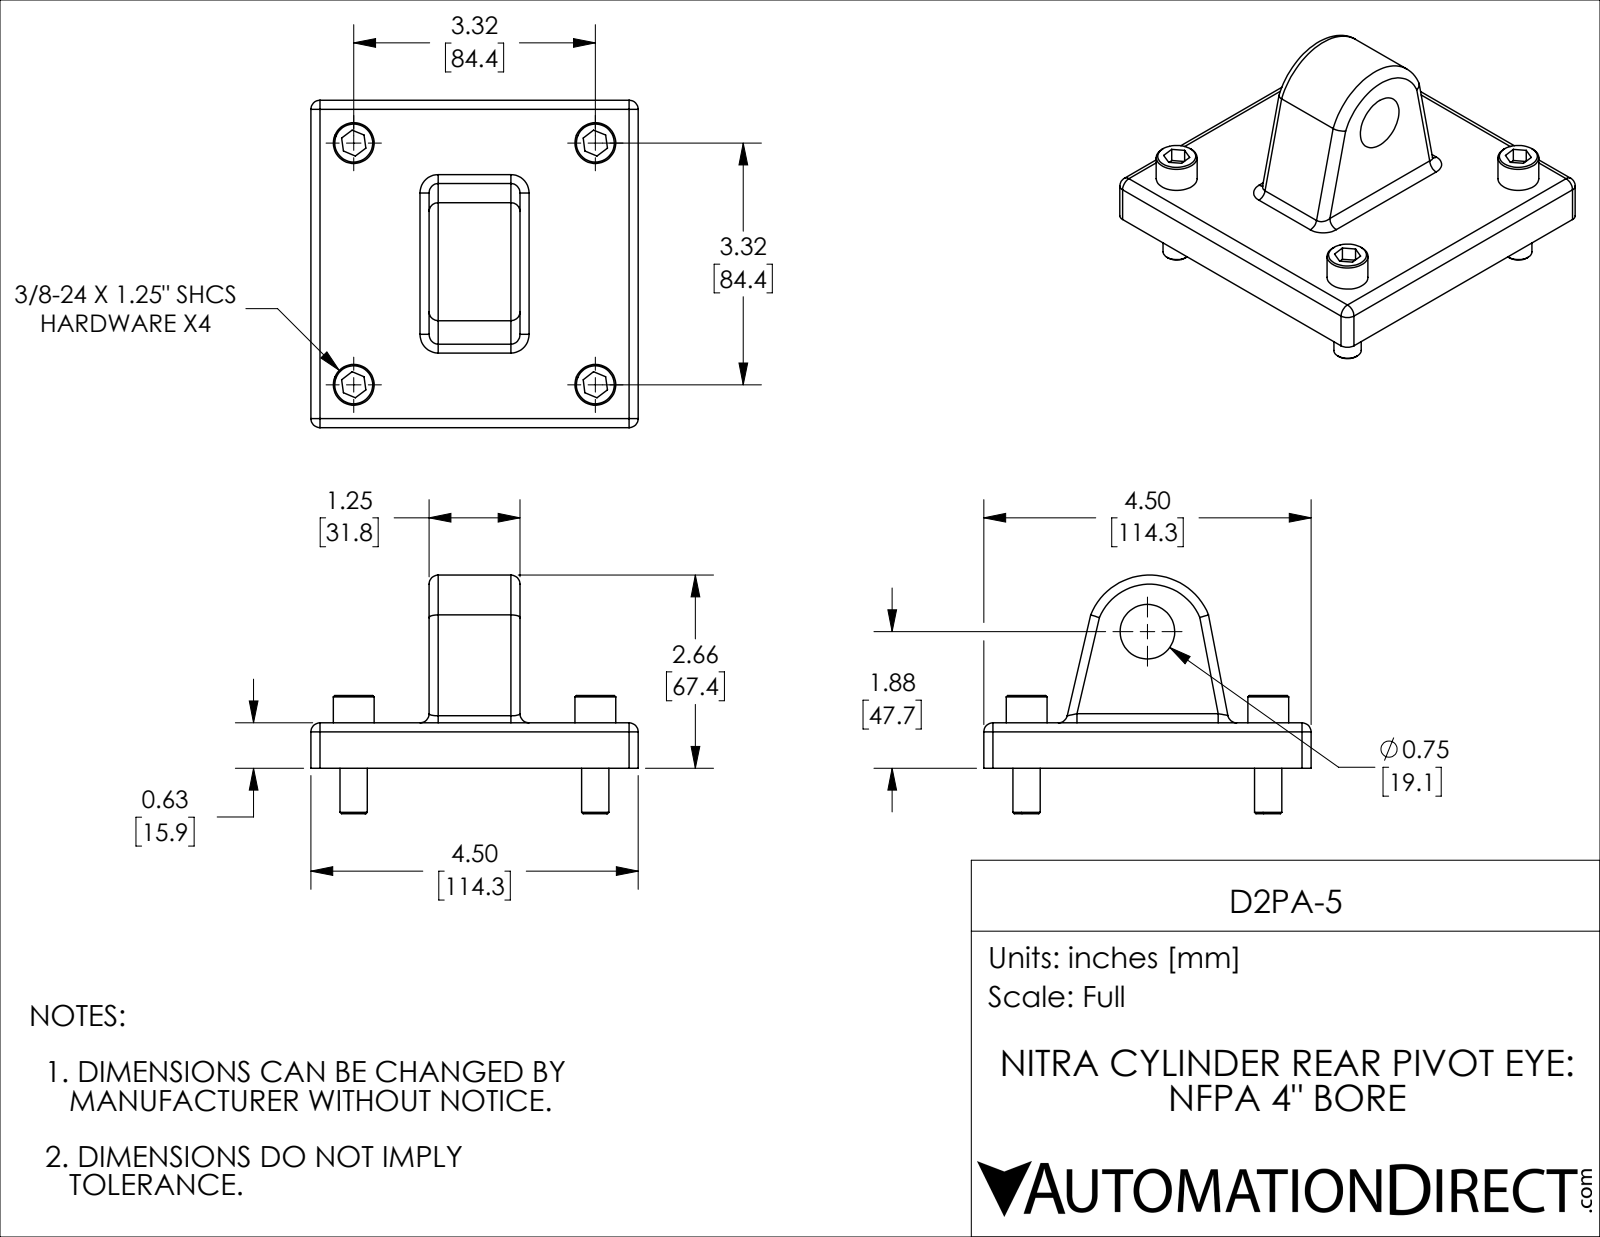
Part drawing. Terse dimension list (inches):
name: D2PA-5
written by: SolidWorks 2019 (CONFIG_CONTROL_DESIGN)
unit: in
bodies: 5 solids, 120 faces (50 planar, 43 cylindrical, 27 other)
size: 4.5 × 4.5 × 3.28
volume: 16.95 in³; area: 75.8 in²
holes: 4× ⌀0.406, 1× ⌀0.751
bosses: 4× ⌀0.562, 4× ⌀0.375
rounds: 16× R0.125, 1× R0.875
face distances: 0.625, 1.625, 2.875, 4.5, 1.25, 0.375, 1, 1.625, 1.25, 0.625
hole spacings: 3.322, 4.698
